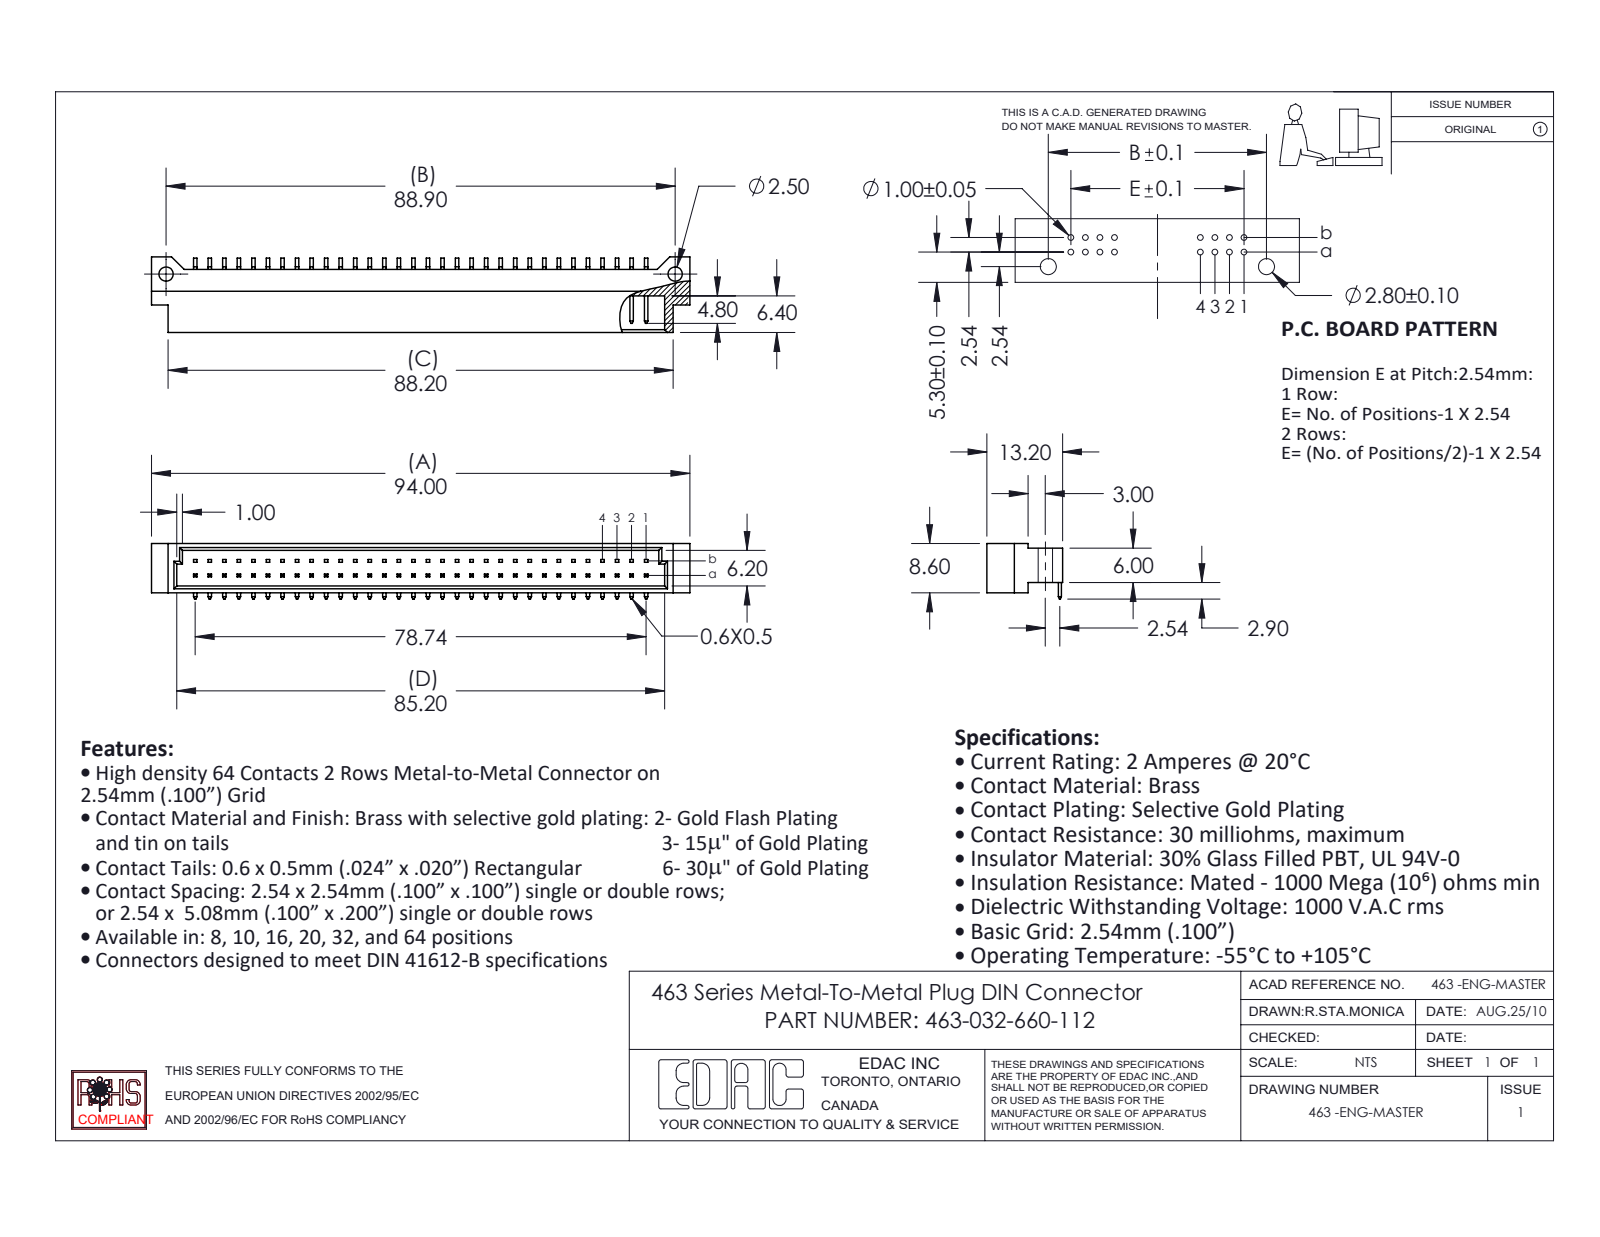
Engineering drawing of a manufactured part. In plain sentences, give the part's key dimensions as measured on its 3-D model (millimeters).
The part is named "463-290-1; 463-032-660-112; 463 Part_64". Its 3-D file was written by "SolidWorks 2020 (CONFIG_CONTROL_DESIGN)". It is 33 solids with 871 faces: 803 planar, 68 cylindrical and 0 other. Overall it measures 94 by 13.2 by 9.7 millimeters. Its volume is 4 463 cubic millimeters and its surface area 6 700 square millimeters. Round holes: 2 of diameter 2.5. Partial cylindrical surfaces (rounded edges, fillets, slot ends): 1 of radius 1.02, 1 of radius 1.52. The main face-to-face distances are 1.2, 7.4, 8.6, 0.8, 6.2, 4.6, 6, 6.8, 0.5, 5.6. The hole center spacings are 88.9.
